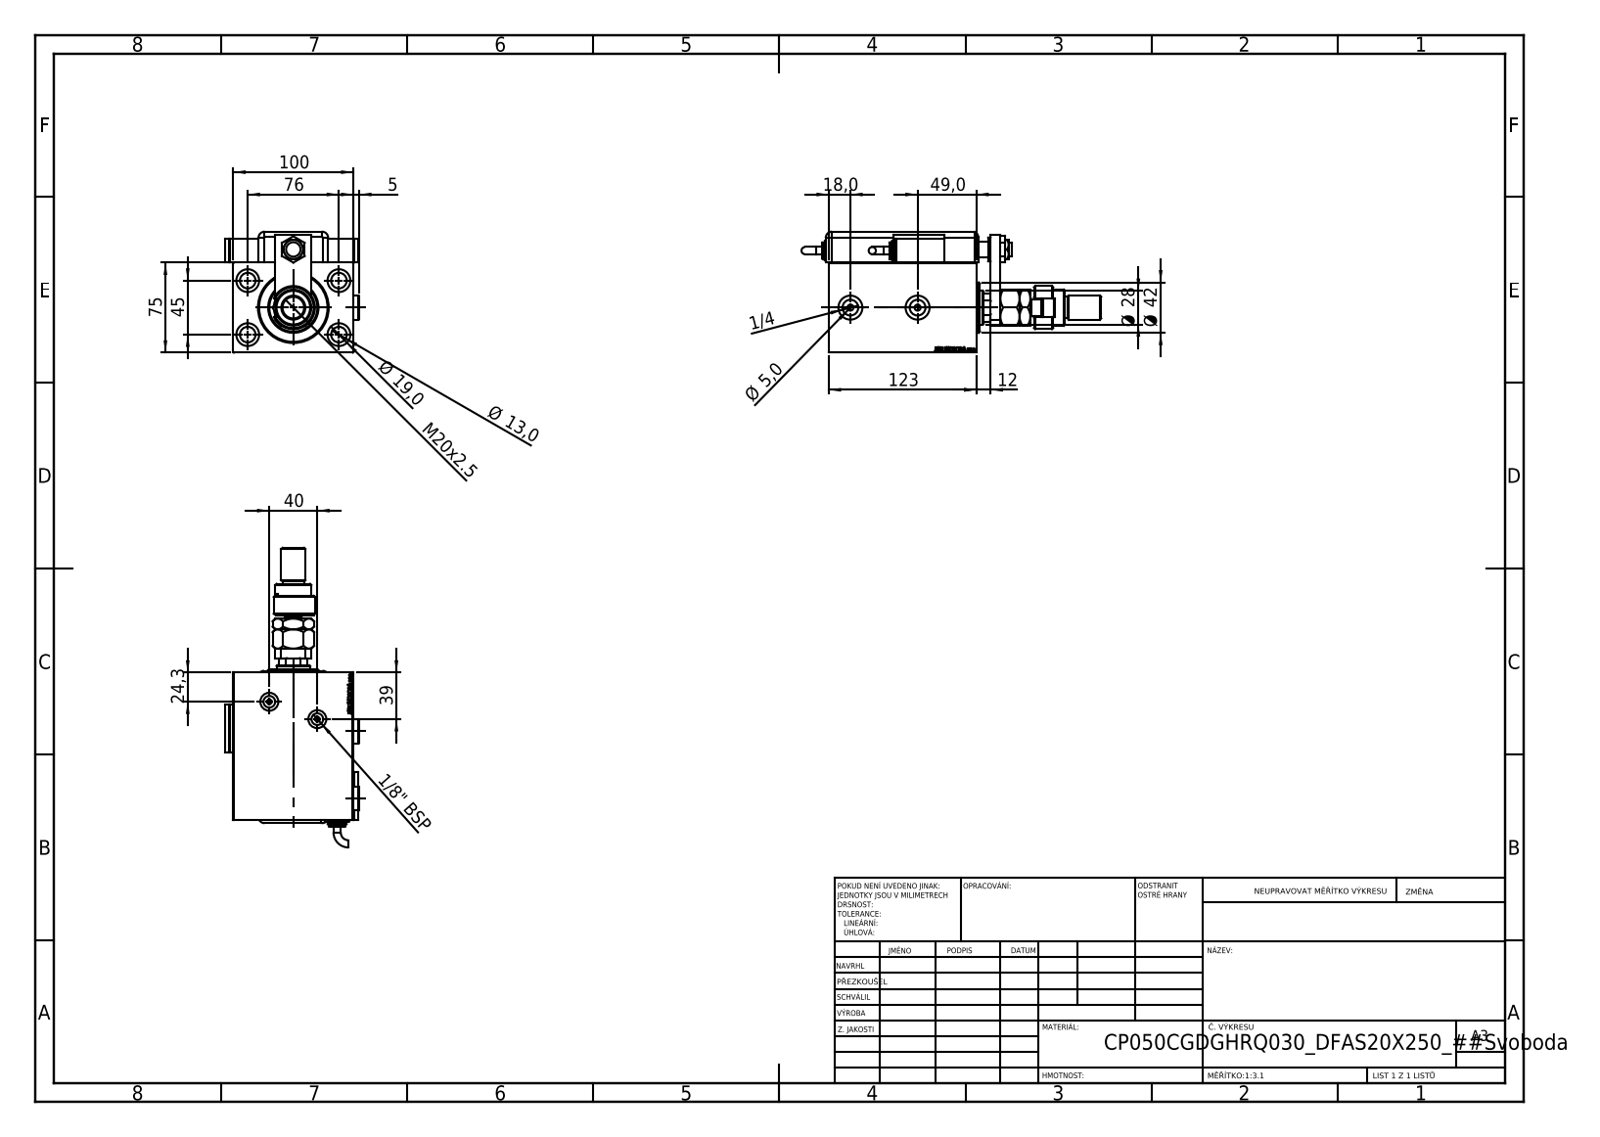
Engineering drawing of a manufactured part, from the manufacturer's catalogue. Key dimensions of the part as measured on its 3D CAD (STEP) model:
Part name (STEP PRODUCT): SWITCH DIM A_G; SWITCH_Q_FRONT_BACK; V450CP_C; TYC (+7 more)
STEP written by: SolidWorks 2019 (CONFIG_CONTROL_DESIGN)
Units: millimetres
Bodies: 17 solids, 1412 faces (683 planar, 160 cylindrical, 569 other)
Overall size (bounding box): 249.76 × 111.9 × 100.8
Volume: 997 919 mm³ · Surface area: 210 388 mm²
Round holes (diameter × count): ⌀13 ×5, ⌀4 ×4, ⌀19 ×4, ⌀20 ×3, ⌀5 ×2, ⌀8 ×2, ⌀9.73 ×2, ⌀13.16 ×2, ⌀15 ×2, ⌀12 ×1, ⌀14 ×1, ⌀18.5 ×1
Round bosses / shafts (diameter × count): ⌀20 ×3, ⌀14 ×3, ⌀16 ×2, ⌀6 ×2, ⌀42 ×1, ⌀36 ×1, ⌀30 ×1, ⌀22 ×1
Partial cylindrical surfaces — rounded edges, fillets, slot ends (radius × count): R5 ×9, R7.5 ×1, R10 ×1, R12 ×1, R13.5 ×1
Main face-to-face distances: 75, 3, 100, 20, 100.8, 25.8, 14, 123, 109, 30
Hole centre spacings: 44.16, 45, 46.04, 76, 80.53, 88.32, 18.28, 20
